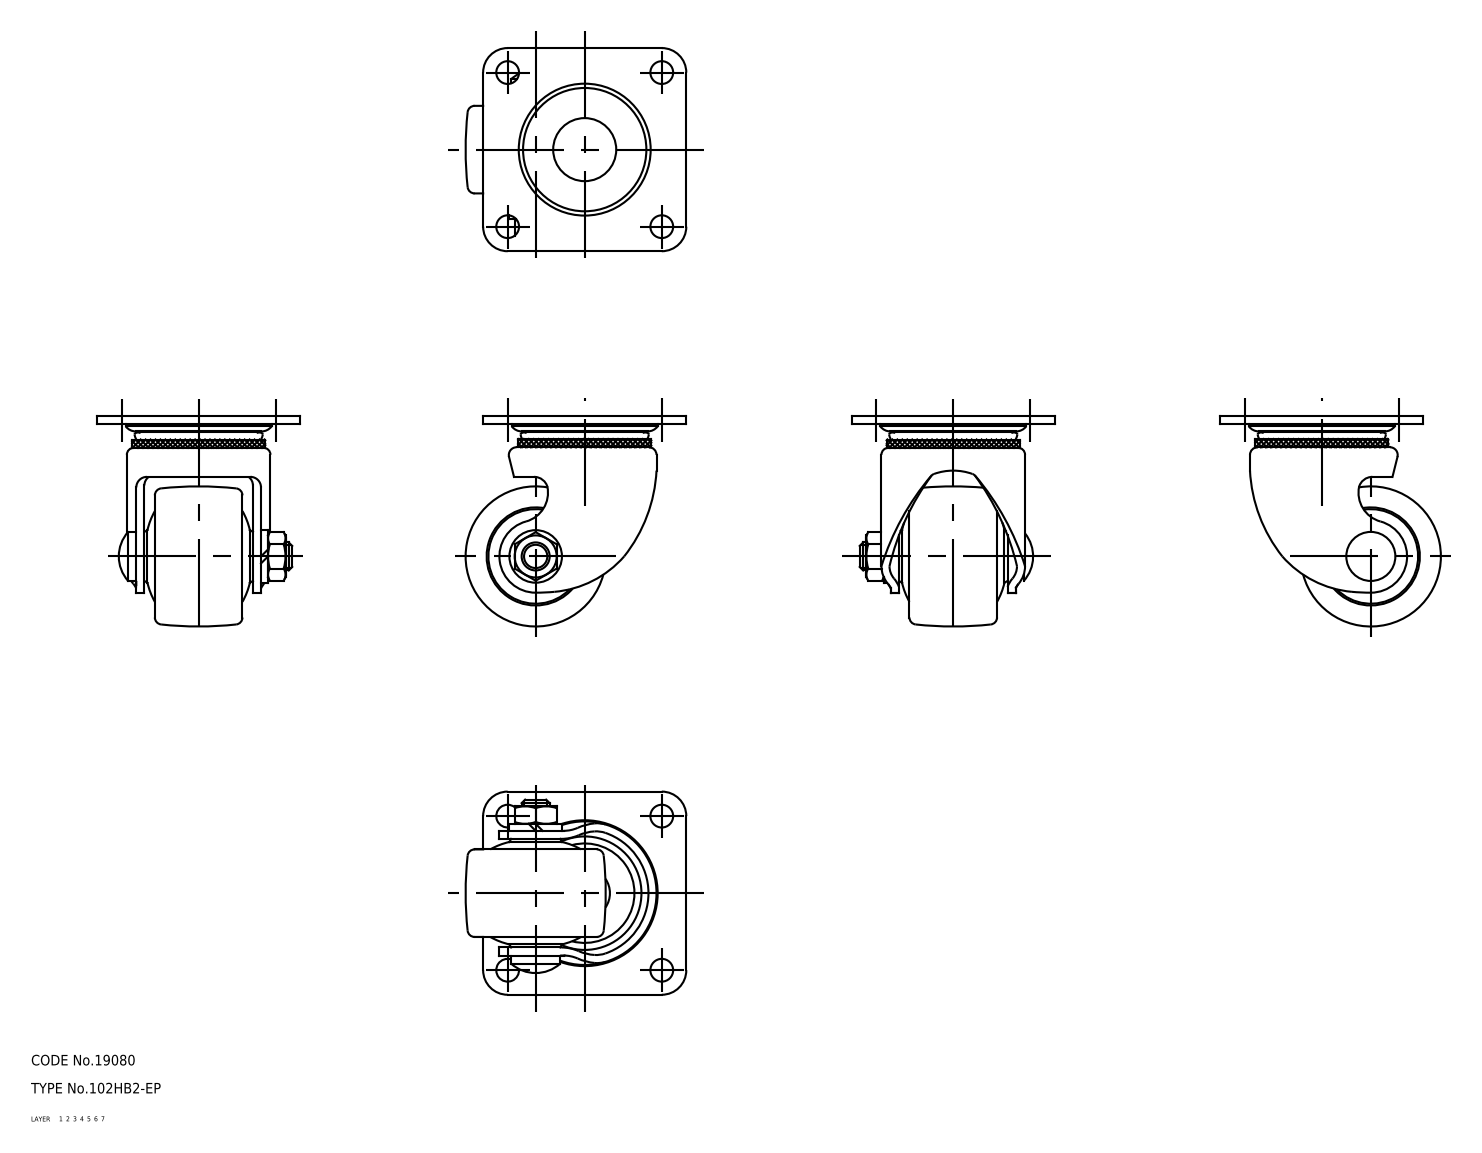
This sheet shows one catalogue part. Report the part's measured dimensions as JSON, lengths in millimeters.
{"part_name": "wheel; mounting plate; main shaft; axle (+1 more)", "step_written_by": "CADfix (AUTOMOTIVE_DESIGN)", "units": "millimeters", "bodies": {"solids": 5, "faces": 230, "planar": 0, "cylindrical": 0, "other": 230}, "overall_size": [63, 60, 58], "volume_mm3": 58462, "surface_area_mm2": 27279}
